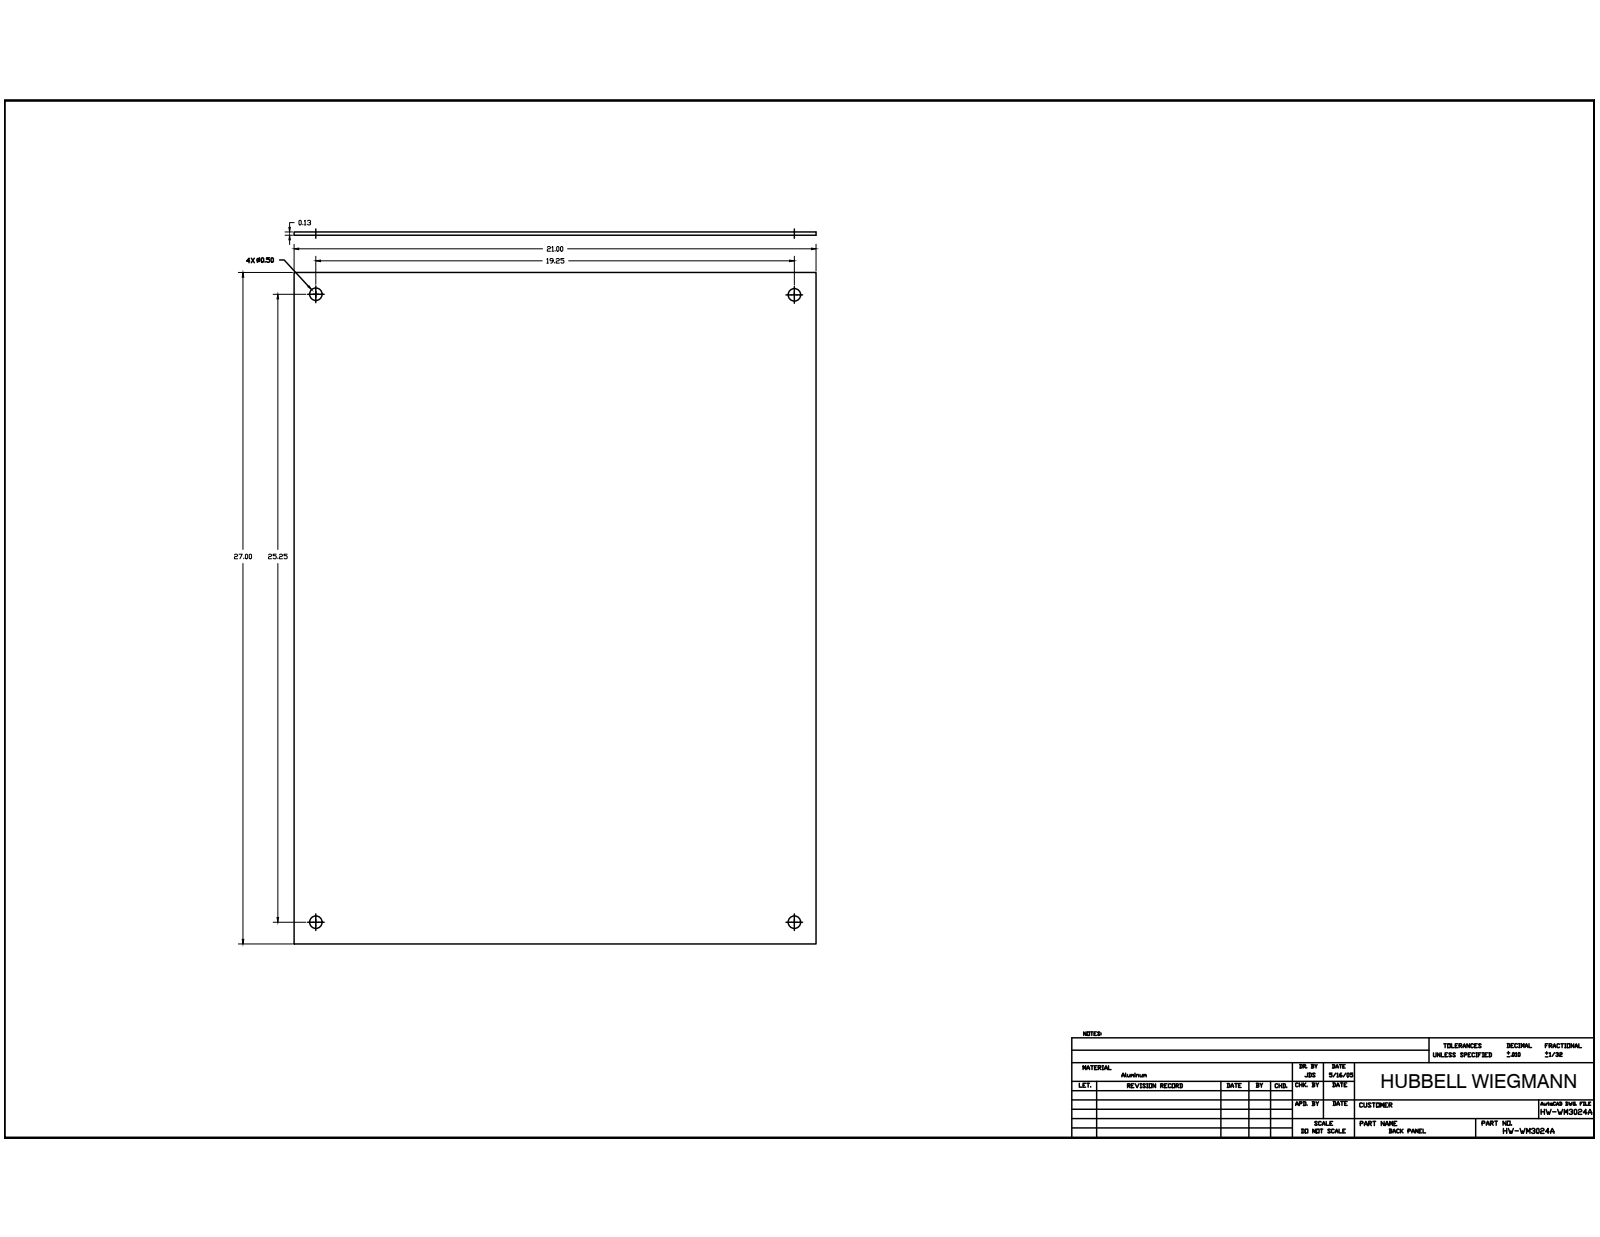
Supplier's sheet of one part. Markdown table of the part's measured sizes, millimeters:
| quantity | value |
| --- | --- |
| part name | BP3024AL_STP |
| STEP written by | Autodesk Inventor 2014 (AUTOMOTIVE_DESIGN) |
| units | millimeters |
| bodies | 1 solid, 10 faces (6 planar, 4 cylindrical, 0 other) |
| overall size | 685.8 × 533.4 × 3.3 |
| volume | 1 206 000 mm³ |
| surface area | 739 177 mm² |
| round holes (diameter × count) | 12.7 × 4 |
| main face-to-face distances | 3.3, 533.4, 685.8 |
| hole center spacings | 488.94, 641.34, 806.46 |
